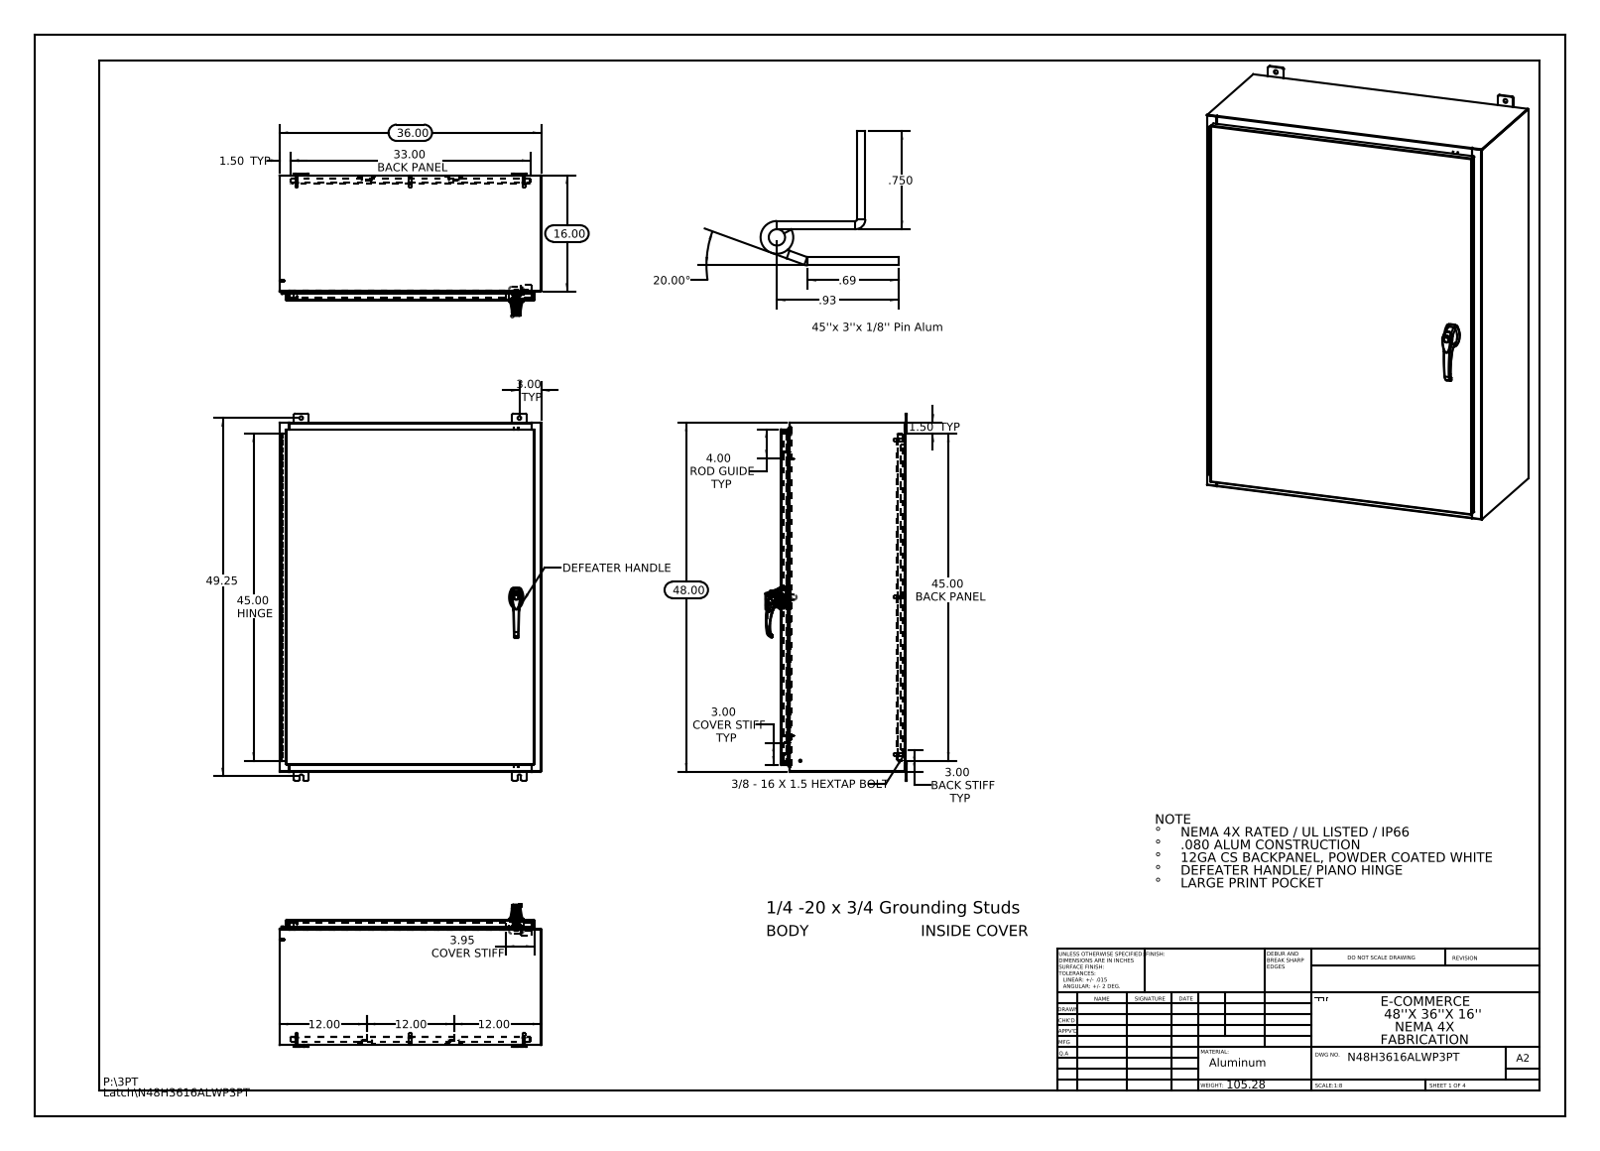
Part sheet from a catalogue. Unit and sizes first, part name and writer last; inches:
Units: inches
Overall size (bounding box): 50.5 × 36 × 19.495
Round holes (diameter × count): ⌀0.5 ×12, ⌀0.25 ×10, ⌀0.138 ×3, ⌀0.161 ×3, ⌀0.079 ×2, ⌀0.203 ×2, ⌀0.313 ×2, ⌀0.437 ×2, ⌀0.125 ×1, ⌀0.125 ×1, ⌀0.197 ×1, ⌀0.276 ×1
Round bosses / shafts (diameter × count): ⌀0.157 ×10, ⌀0.14 ×10, ⌀0.625 ×8, ⌀0.375 ×8, ⌀0.33 ×8, ⌀0.315 ×3, ⌀0.236 ×3, ⌀1.181 ×1
Partial cylindrical surfaces — rounded edges, fillets, slot ends (radius × count): R0.118 ×37, R0.013 ×34, R0.006 ×33, R0.088 ×28, R0.19 ×24, R0.039 ×15, R0.028 ×12, R0.008 ×6
Main face-to-face distances: 0.075, 17.126, 17.051, 17.201, 0.104, 35.925, 1, 16.126, 1.075, 16.051
Hole centre spacings: 17.357, 19.665, 21.625, 38.003, 45.986, 31.25, 43.25, 0.295
Volume: 706.2 in³ · Surface area: 17 651 in²
Bodies: 51 solids, 3400 faces (1309 planar, 1305 cylindrical, 786 other)
Part name (STEP PRODUCT): N48H3616ALWP3PT Cover; 00005310_26163101; N48H3616ALWP3PT; N48H3616ALWP3PT Hinge Enclosure Side2 (+8 more)
STEP written by: SolidWorks 2013 (CONFIG_CONTROL_DESIGN)
